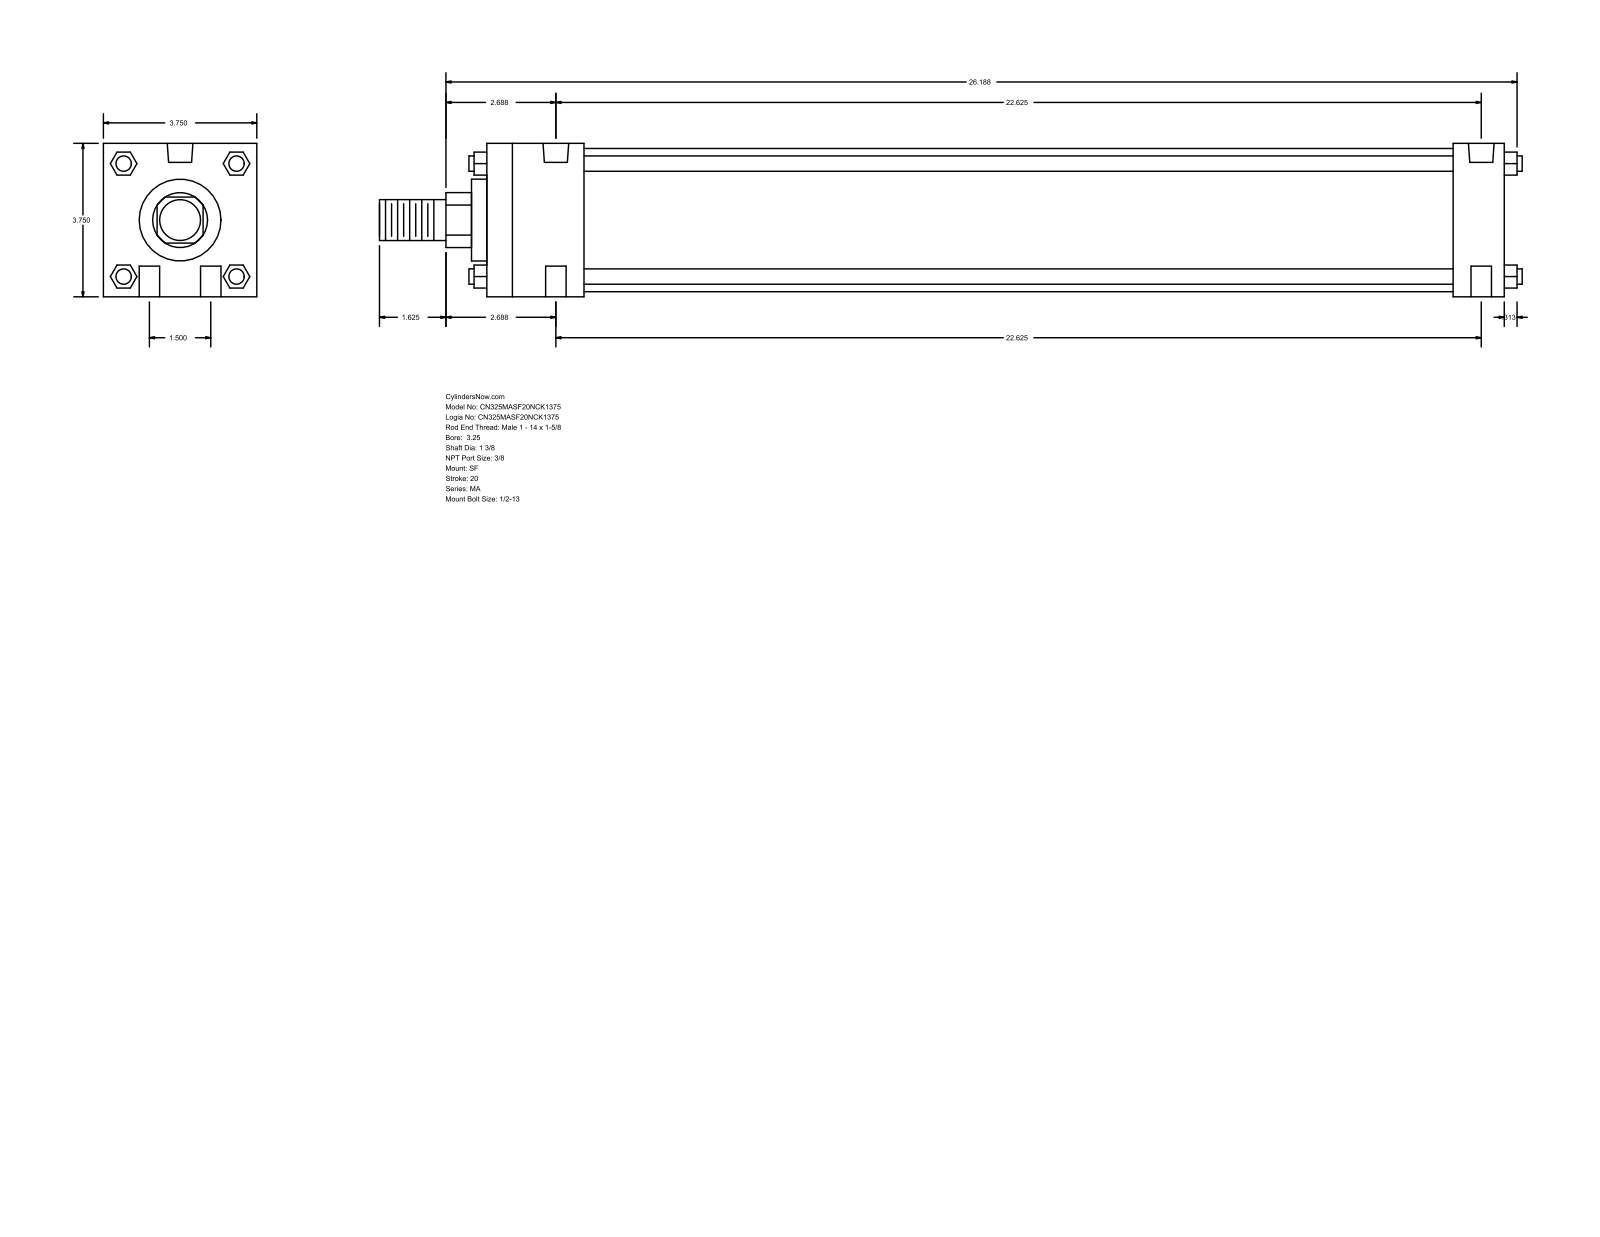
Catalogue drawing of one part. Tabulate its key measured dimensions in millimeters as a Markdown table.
| quantity | value |
| --- | --- |
| part name | MA_SF__0325_1.375 |
| STEP written by | GSSL Pune (CONFIG_CONTROL_DESIGN) |
| units | millimeters |
| bodies | 0 solids, 124 faces (94 planar, 30 cylindrical, 0 other) |
| overall size | 709.61 × 95.25 × 95.25 |
| round holes (diameter × count) | 12.7 × 4, 11.11 × 2, 15.93 × 2 |
| round bosses / shafts (diameter × count) | 9.53 × 4, 88.9 × 1, 50.8 × 1, 34.92 × 1, 25.4 × 1 |
| partial cylindrical surfaces (radius × count) | 17.06 × 1 |
| main face-to-face distances | 95.24, 631.83, 600.08, 31.75, 60.32, 539.76, 571.51, 9.52, 69.84, 609.6 |
| hole center spacings | 19.05, 575, 574.68, 38.1, 575.94, 565.14 |
